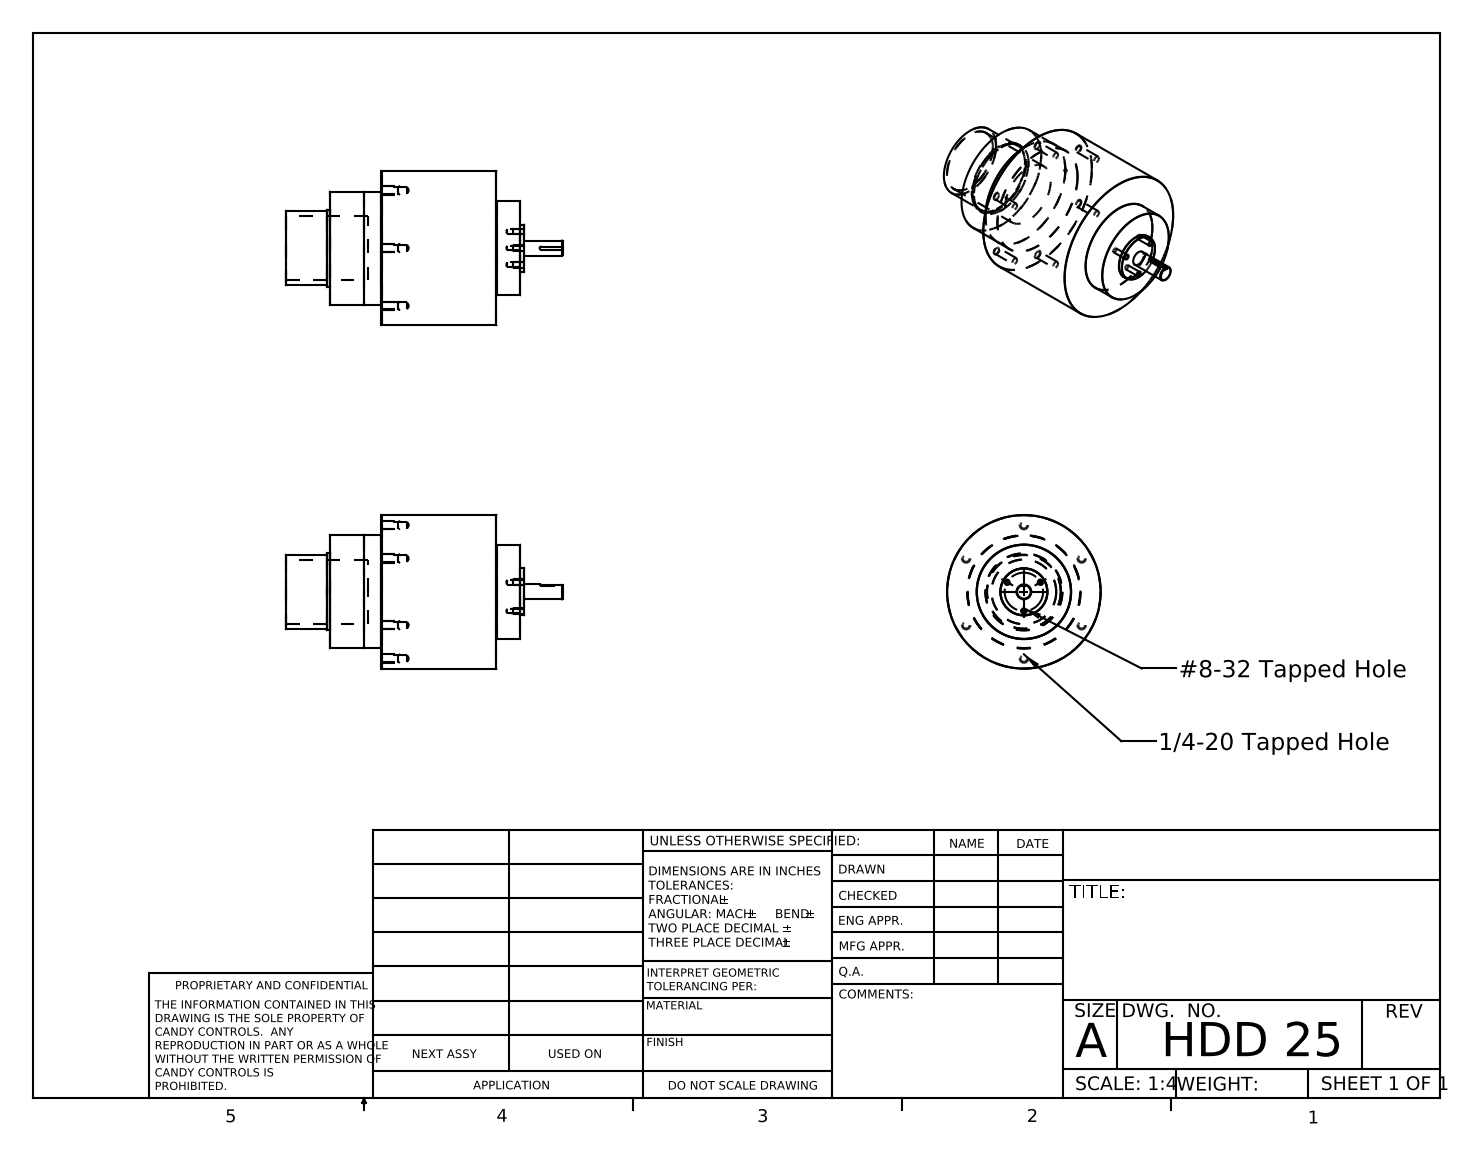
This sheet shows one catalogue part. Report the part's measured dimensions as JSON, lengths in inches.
{"part_name": "HDD 25", "step_written_by": "SolidWorks 2010 (CONFIG_CONTROL_DESIGN)", "units": "inches", "bodies": {"solids": 1, "faces": 98, "planar": 12, "cylindrical": 37, "other": 49}, "overall_size": [8.11, 4.5, 4.5], "volume_in3": 68.86, "surface_area_in2": 129.5, "round_holes": [[0.201, 6], [0.136, 3], [1.89, 1]], "round_bosses_or_shafts": [[4.5, 1], [3.313, 1], [3.303, 1], [2.76, 1], [2.25, 1], [2.165, 1], [1.375, 1], [0.437, 1]], "partial_cylinders_radius": [[0.047, 1]], "face_to_face_distances": [3.37, 1.5, 4.87, 5.56, 4.06, 0.69, 1.1, 0.4, 3.77, 4.46], "hole_center_spacings": [1.741, 1.953, 1.953, 2.287, 3.383, 0.974, 1.391, 0.562]}
